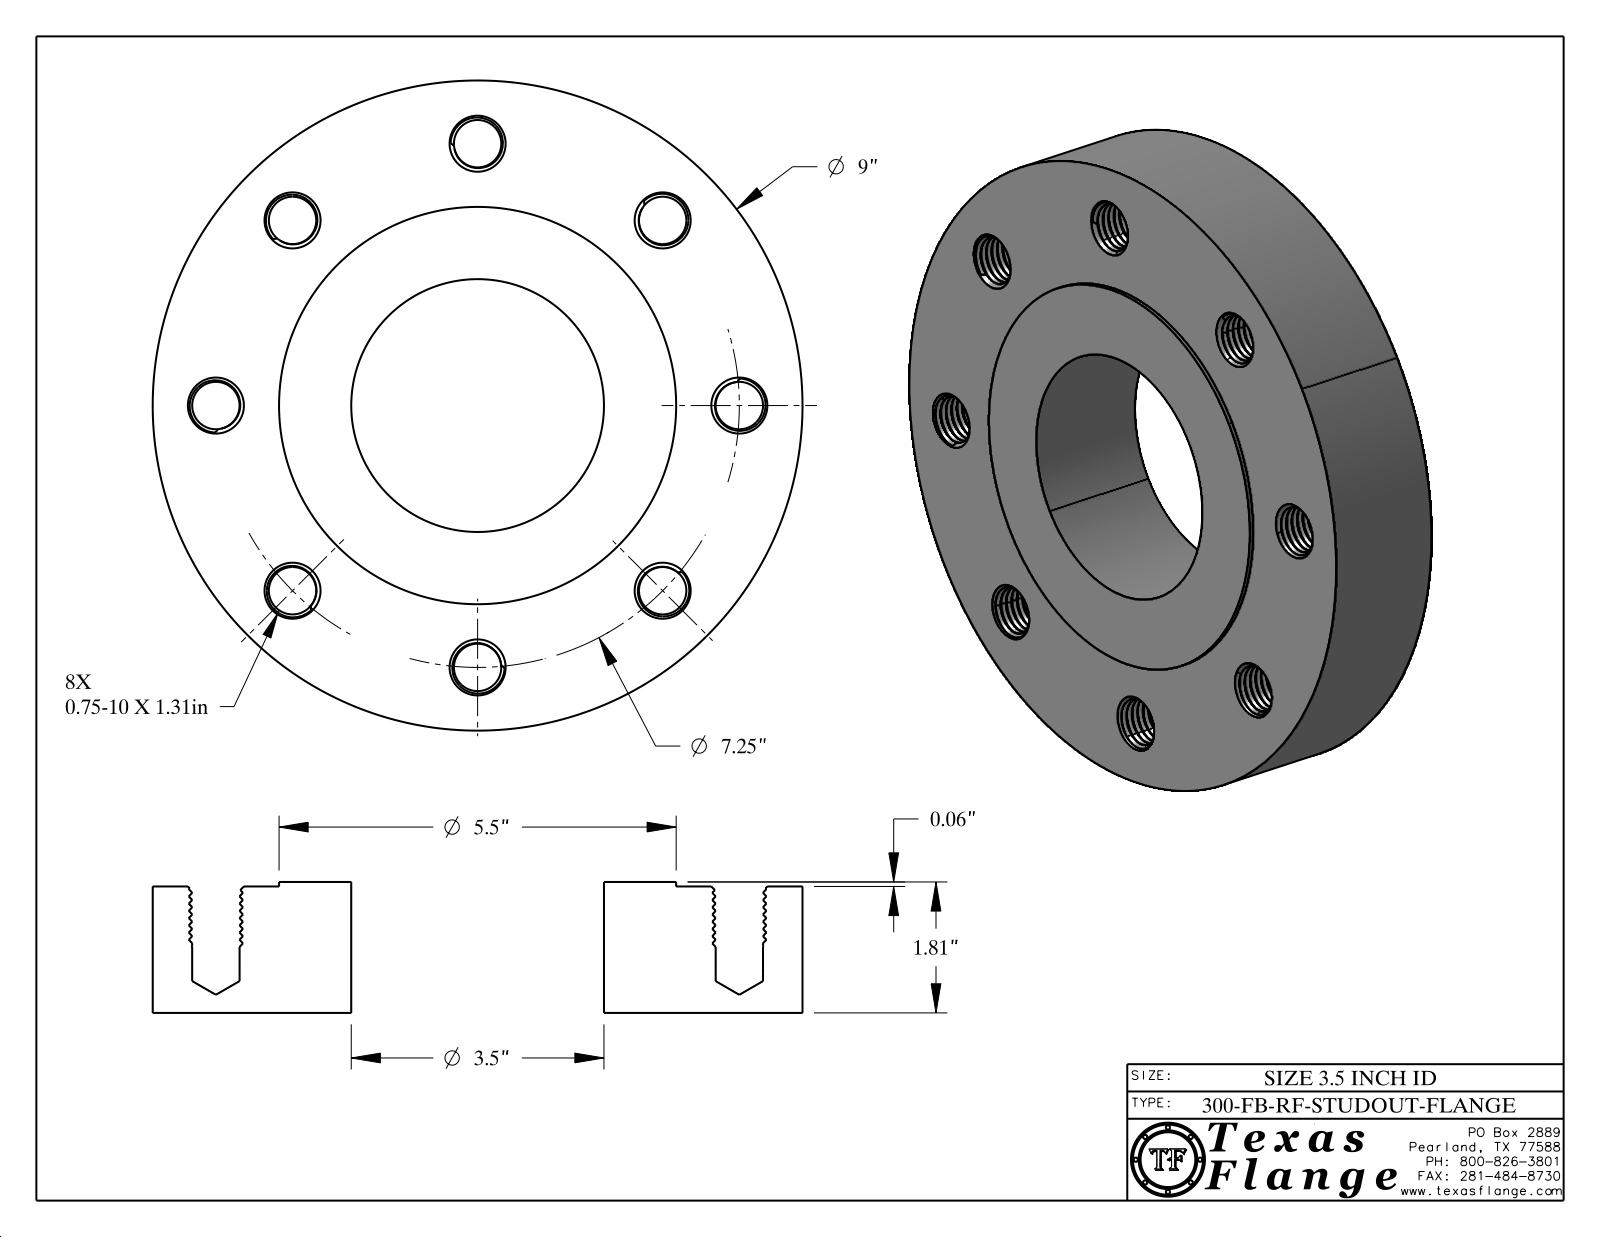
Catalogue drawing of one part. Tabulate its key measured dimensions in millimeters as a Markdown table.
| quantity | value |
| --- | --- |
| part name | 3.5-300-FB-RF-STUDOUT-FLANGE |
| STEP written by | CATIA V5 STEP AP214 (AUTOMOTIVE_DESIGN) |
| units | millimeters |
| bodies | 1 solid, 874 faces (368 planar, 186 cylindrical, 320 other) |
| overall size | 228.6 × 228.6 × 46.1 |
| volume | 1 496 000 mm³ |
| surface area | 133 100 mm² |
| round holes (diameter × count) | 16.7 × 8, 25.4 × 1, 88.9 × 1 |
| round bosses / shafts (diameter × count) | 1.5 × 8, 228.6 × 1, 139.7 × 1, 20 × 1 |
| main face-to-face distances | 44.5, 1.6, 46.1, 0.4, 45.7, 44.1, 7.6, 7.4, 1.4, 6.3 |
| hole center spacings | 70.5, 92.1, 130.2, 170.1, 184.2 |
